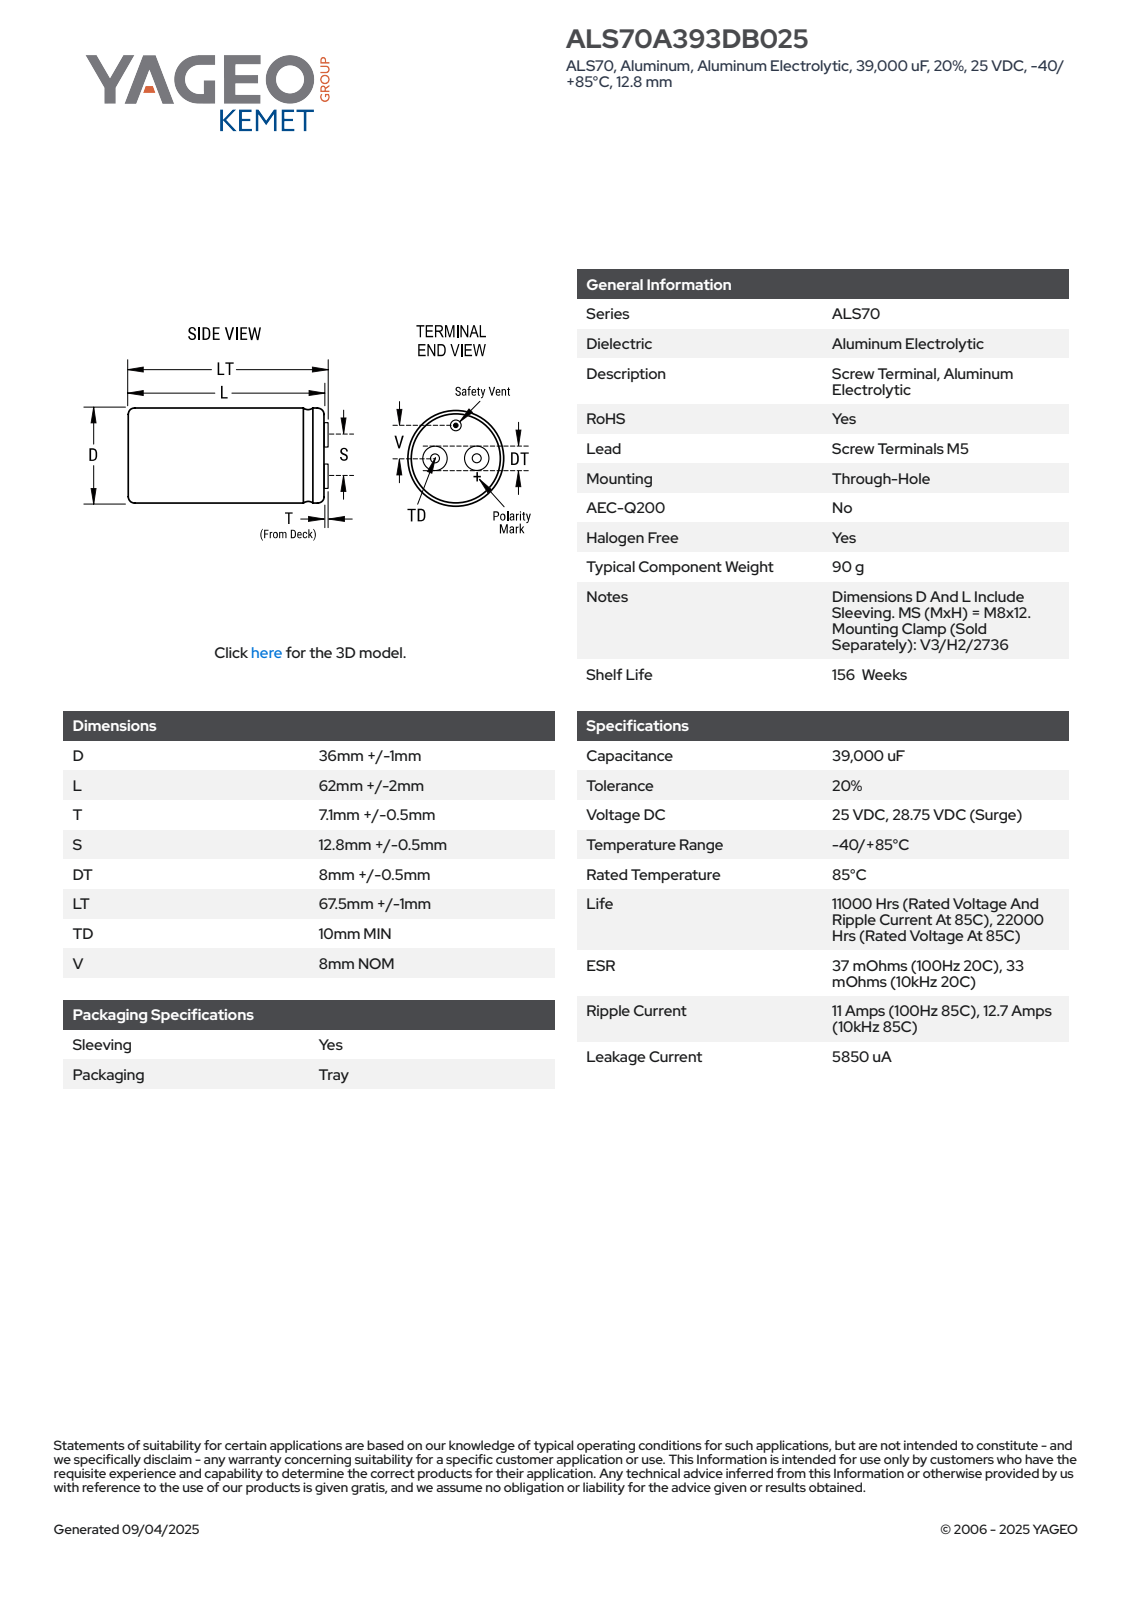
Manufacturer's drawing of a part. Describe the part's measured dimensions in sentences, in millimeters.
The part is named "CARC_KAR_36X62_D37L64T7.6S12.8DT8.500TD10.000V8.000". Its 3-D file was written by "SolidWorks 2014 (AUTOMOTIVE_DESIGN)". It is 1 solid with 88 faces: 30 planar, 19 cylindrical and 39 other. Overall it measures 71.6 by 37.01 by 37 millimeters. Its volume is 68 933 cubic millimeters and its surface area 10 124 square millimeters. Round holes: 2 of diameter 5, 1 of diameter 1.33. Round bosses or shafts: 2 of diameter 8.5, 1 of diameter 37, 1 of diameter 2.27. Partial cylindrical surfaces (rounded edges, fillets, slot ends): 1 of radius 18.51. The main face-to-face distances are 64, 71.6, 7.6, 61.6, 2.4, 10, 64.35, 2.75, 0.35, 7.25. The hole center spacings are 10.24, 12.8.
